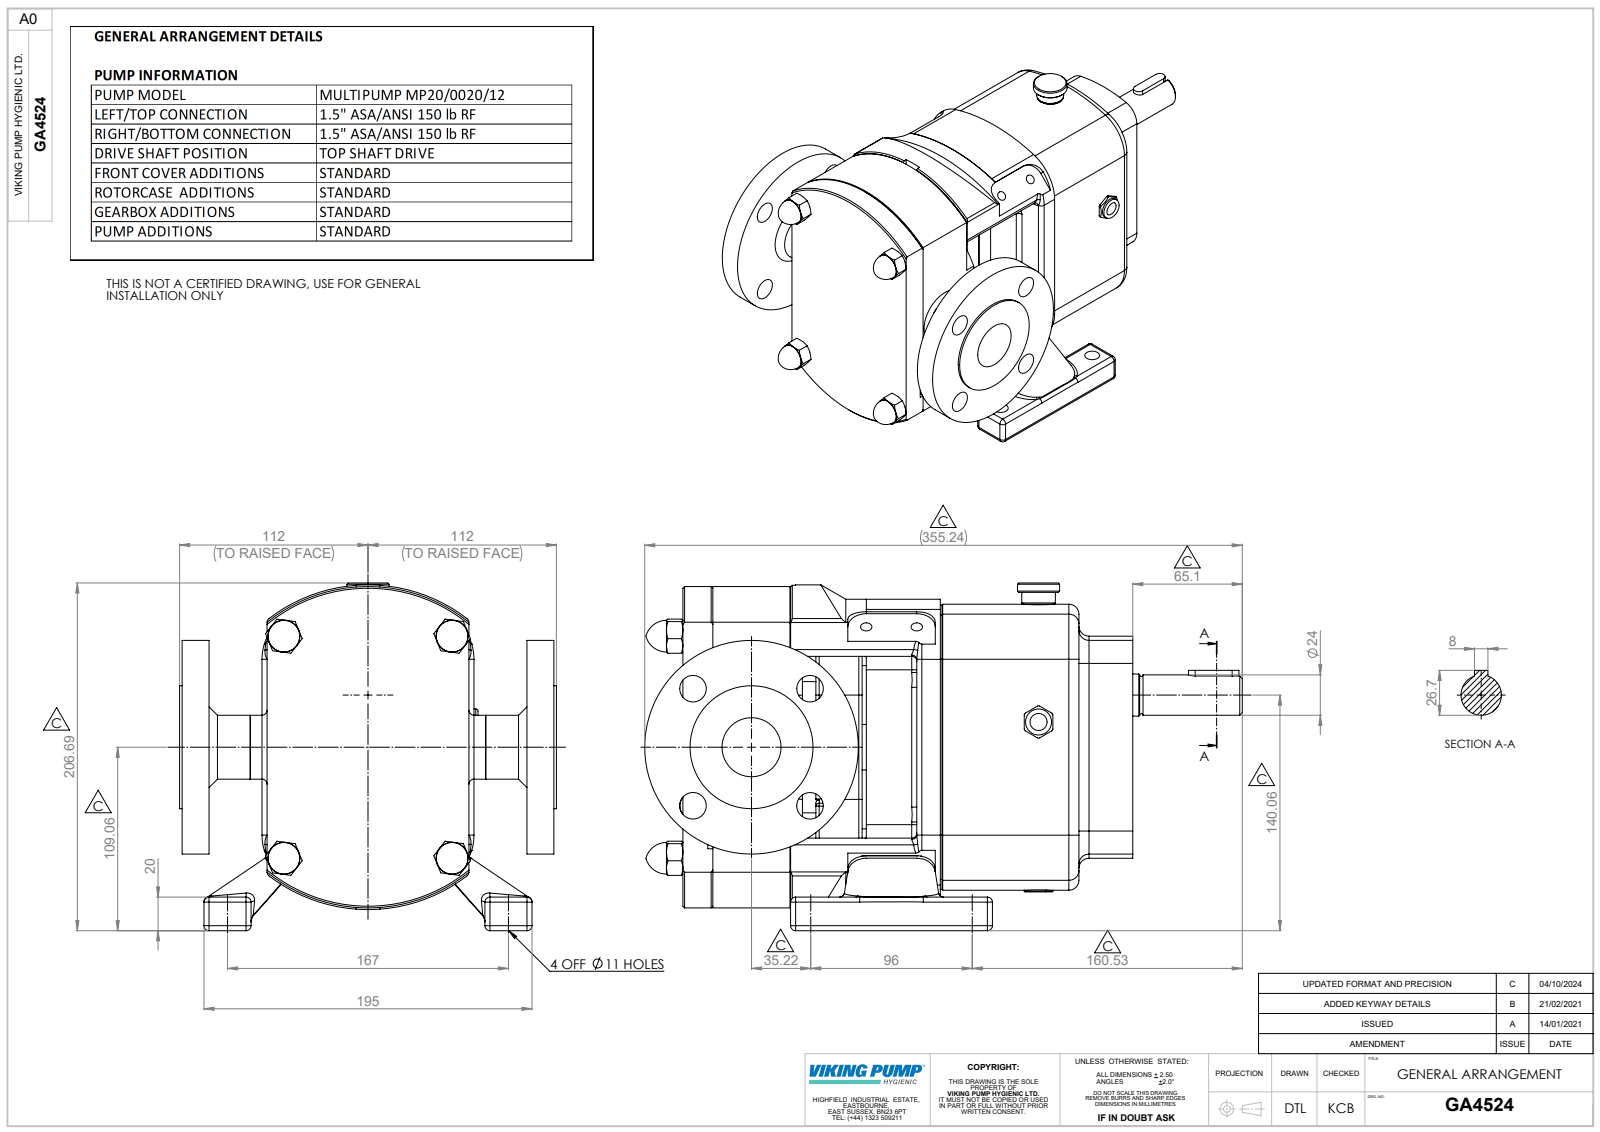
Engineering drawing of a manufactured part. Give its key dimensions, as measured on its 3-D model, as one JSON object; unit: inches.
{"part_name": "GA4524; Copy of CP20-0020-12 H T^GA4524; Copy of Z94-5301-22 - 1.5 INCH ASA 150^GA4524", "step_written_by": "SolidWorks 2023 (AUTOMOTIVE_DESIGN)", "units": "inches", "bodies": {"solids": 3, "faces": 829, "planar": 255, "cylindrical": 304, "other": 270}, "overall_size": [13.986, 8.819, 8.137], "volume_in3": 312, "surface_area_in2": 556.9, "round_holes": [[0.622, 6], [0.268, 4], [0.433, 4], [0.255, 3], [0.315, 2], [0.887, 1], [1.382, 1]], "round_bosses_or_shafts": [[1.378, 2], [0.669, 2], [5, 1], [2.878, 1], [1.496, 1], [0.985, 1], [0.984, 1], [0.945, 1]], "partial_cylinders_radius": [[0.118, 55], [0.079, 18], [0.039, 16], [0.236, 8], [0.437, 8], [0.05, 6], [0.157, 6], [0.315, 6]], "face_to_face_distances": [1.358, 6.083, 4.724, 0.63, 1.988, 6.713, 8.071, 7.441, 4.293, 6.236], "hole_center_spacings": [1.937, 2.739, 2.114, 1.183, 1.937, 2.738, 2.741, 3.636]}
